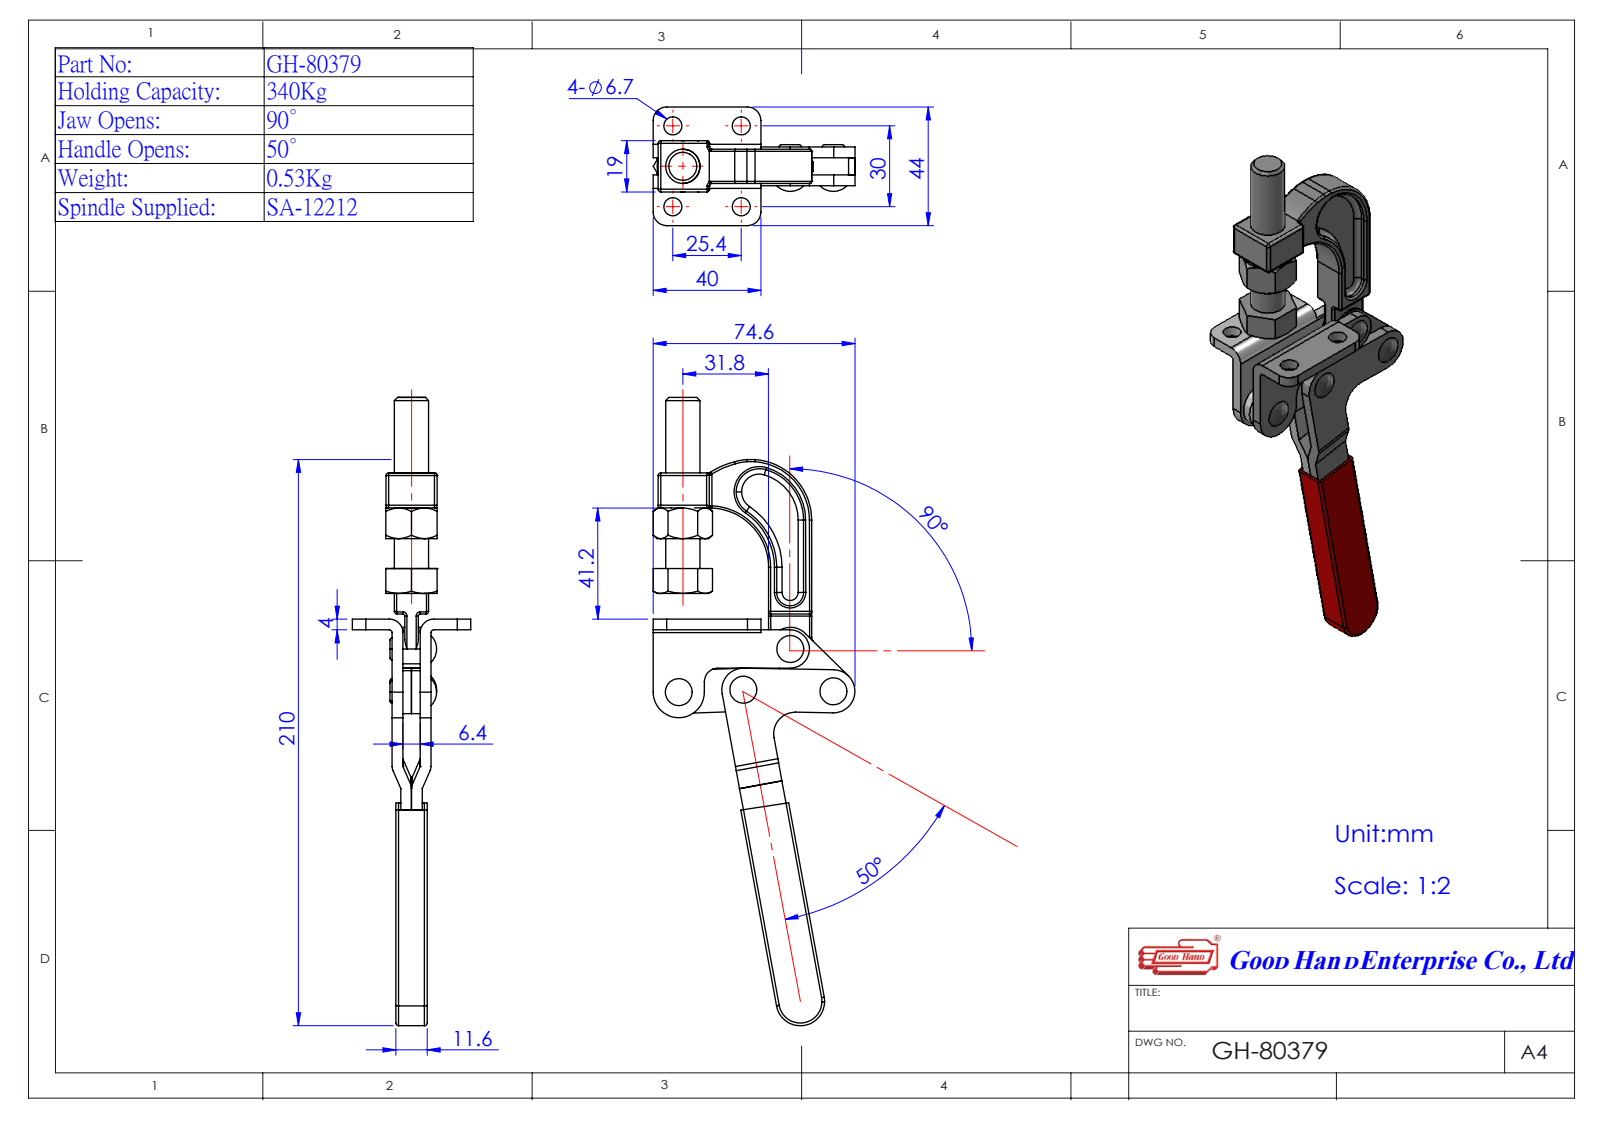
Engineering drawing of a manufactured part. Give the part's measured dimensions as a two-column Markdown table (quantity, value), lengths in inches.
| quantity | value |
| --- | --- |
| part name | Group3^EMC80379; Group2^EMC80379; EMC80379; Group4^EMC80379 (+1 more) |
| STEP written by | SolidWorks 2016 (AUTOMOTIVE_DESIGN) |
| units | inches |
| bodies | 3 solids, 238 faces (119 planar, 83 cylindrical, 36 other) |
| overall size | 9.178 × 2.949 × 1.732 |
| volume | 2.831 in³ |
| surface area | 56.48 in² |
| round holes (diameter × count) | 0.197 × 4, 0.264 × 4 |
| round bosses / shafts (diameter × count) | 0.5 × 1 |
| partial cylindrical surfaces (radius × count) | 0.197 × 6, 0.004 × 4, 0.161 × 4, 0.315 × 4, 0.039 × 2, 0.079 × 1, 0.28 × 1, 0.304 × 1 |
| main face-to-face distances | 0.157, 0.409, 0.252, 0.055, 0.512, 0.102, 0.354, 0.189, 0.567, 0.031 |
| hole center spacings | 1, 1.181, 1.548, 0.883, 0.907, 0.945, 1.317, 1.747 |
